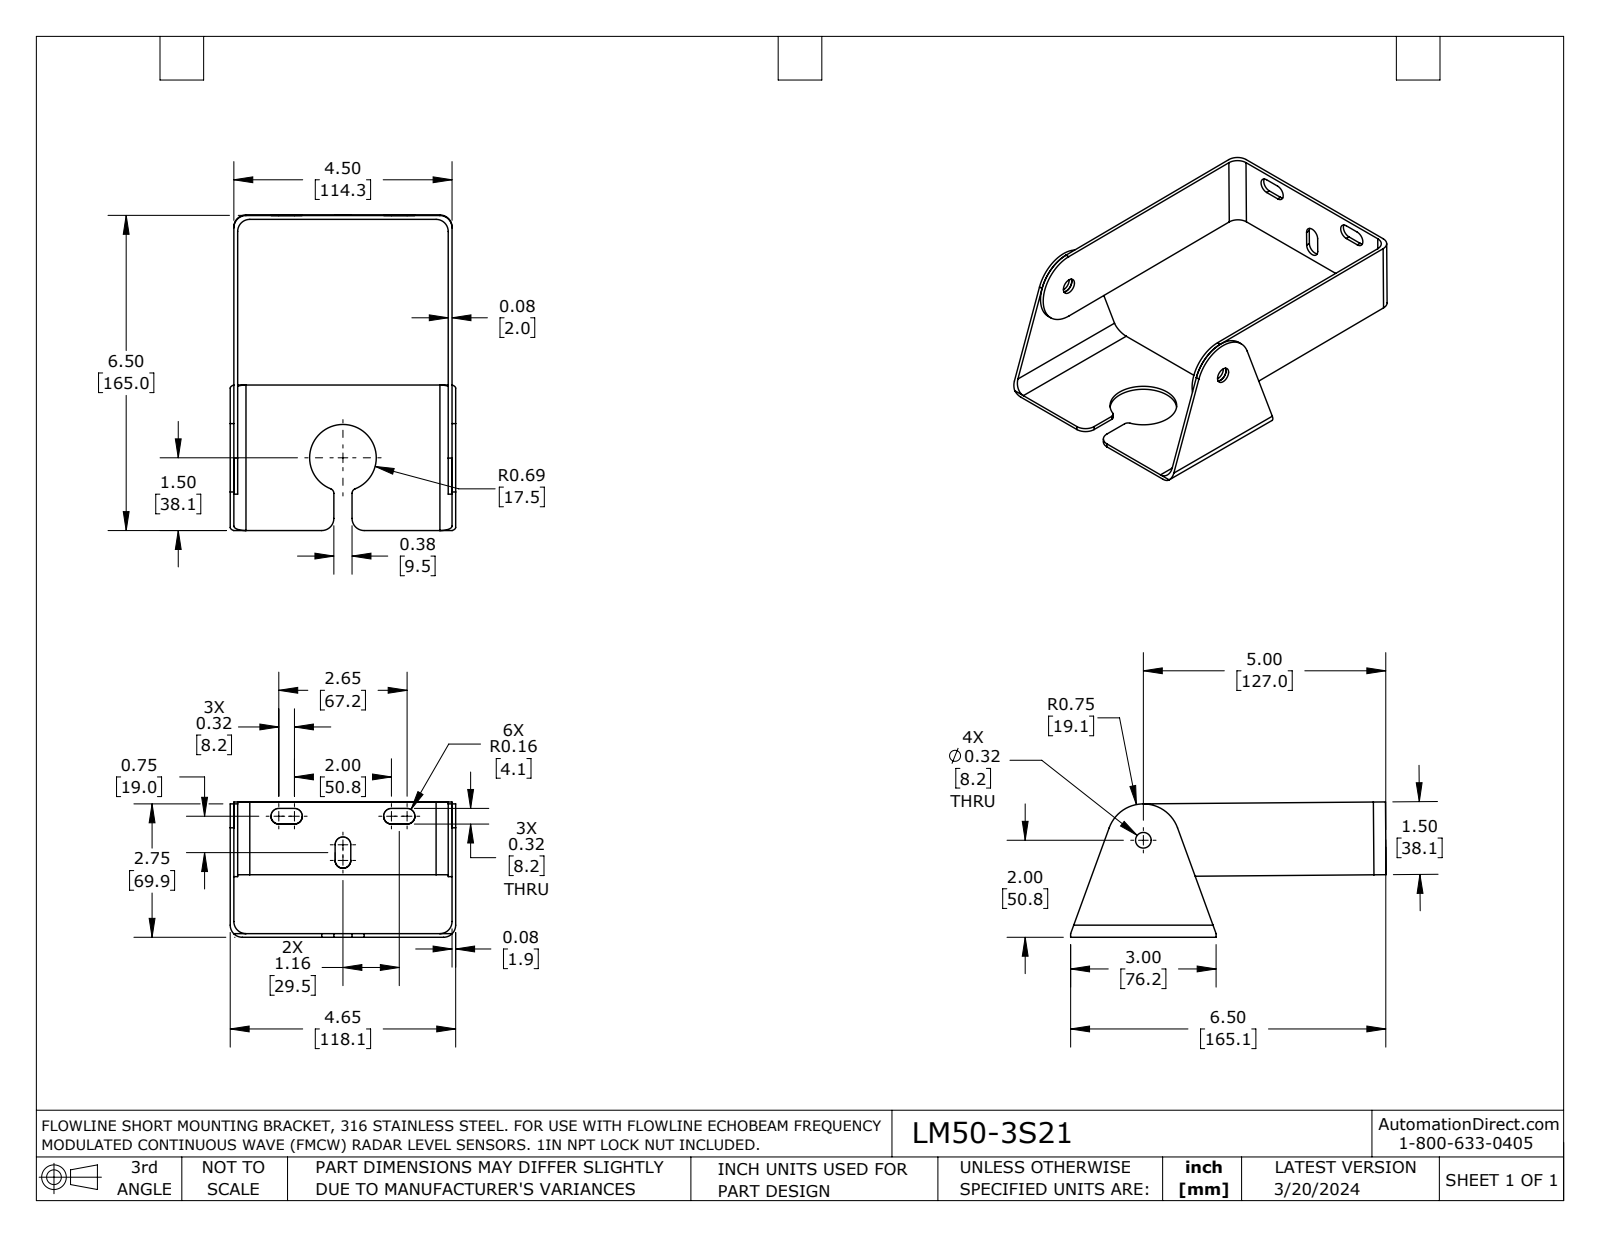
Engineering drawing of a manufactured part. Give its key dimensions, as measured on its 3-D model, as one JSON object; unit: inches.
{"part_name": "LM50-3S21", "step_written_by": "SolidWorks 2021 (AUTOMOTIVE_DESIGN)", "units": "inches", "bodies": {"solids": 2, "faces": 63, "planar": 29, "cylindrical": 34, "other": 0}, "overall_size": [6.506, 4.65, 2.79], "volume_in3": 3.47, "surface_area_in2": 93.75, "round_holes": [[0.323, 1], [1.375, 1]], "partial_cylinders_radius": [[0.25, 10], [0.161, 6], [0.1, 2], [0.75, 1]], "face_to_face_distances": [0.079, 0.075, 4.421, 4.5, 0.154, 4.496, 4.575, 4.343, 4.65, 1.5]}
